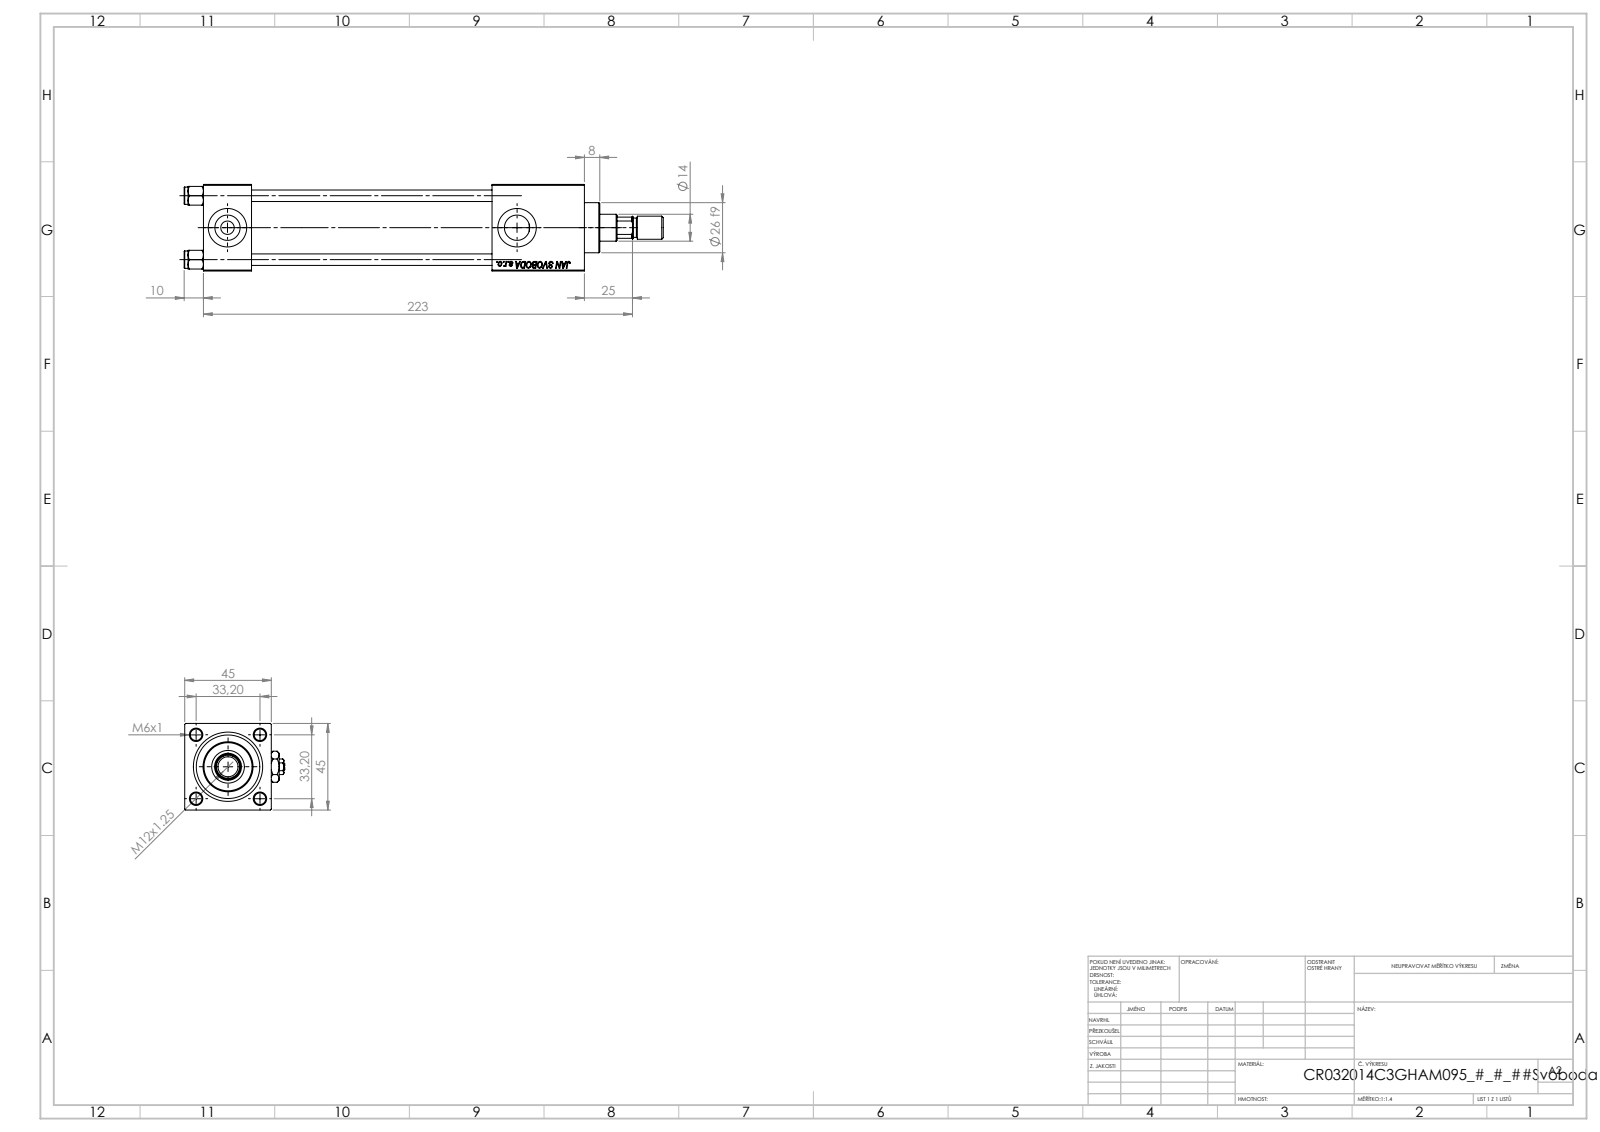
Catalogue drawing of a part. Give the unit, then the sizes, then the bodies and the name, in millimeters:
Units: millimetres
Overall size (bounding box): 249 × 52 × 45
Round holes (diameter × count): ⌀6 ×4, ⌀7 ×2, ⌀13.16 ×2, ⌀20 ×2, ⌀6.5 ×1, ⌀14 ×1, ⌀17 ×1, ⌀24 ×1, ⌀32 ×1, ⌀33 ×1
Round bosses / shafts (diameter × count): ⌀9 ×4, ⌀38 ×1, ⌀26 ×1, ⌀12 ×1, ⌀10 ×1
Partial cylindrical surfaces — rounded edges, fillets, slot ends (radius × count): R6.5 ×1
Main face-to-face distances: 45, 25, 198, 173, 150, 125, 48, 169.3, 144.3, 19.3
Hole centre spacings: 23.48, 33.2, 46.95, 150.5
Volume: 238 836 mm³ · Surface area: 95 222 mm²
Bodies: 14 solids, 1262 faces (576 planar, 102 cylindrical, 584 other)
Part name (STEP PRODUCT): Zatka_pro_OIL_PORT; V215CR_C_TYCINKA; NUT_M5_C; ROD_END_AH (+3 more)
STEP written by: SolidWorks 2019 (CONFIG_CONTROL_DESIGN)
